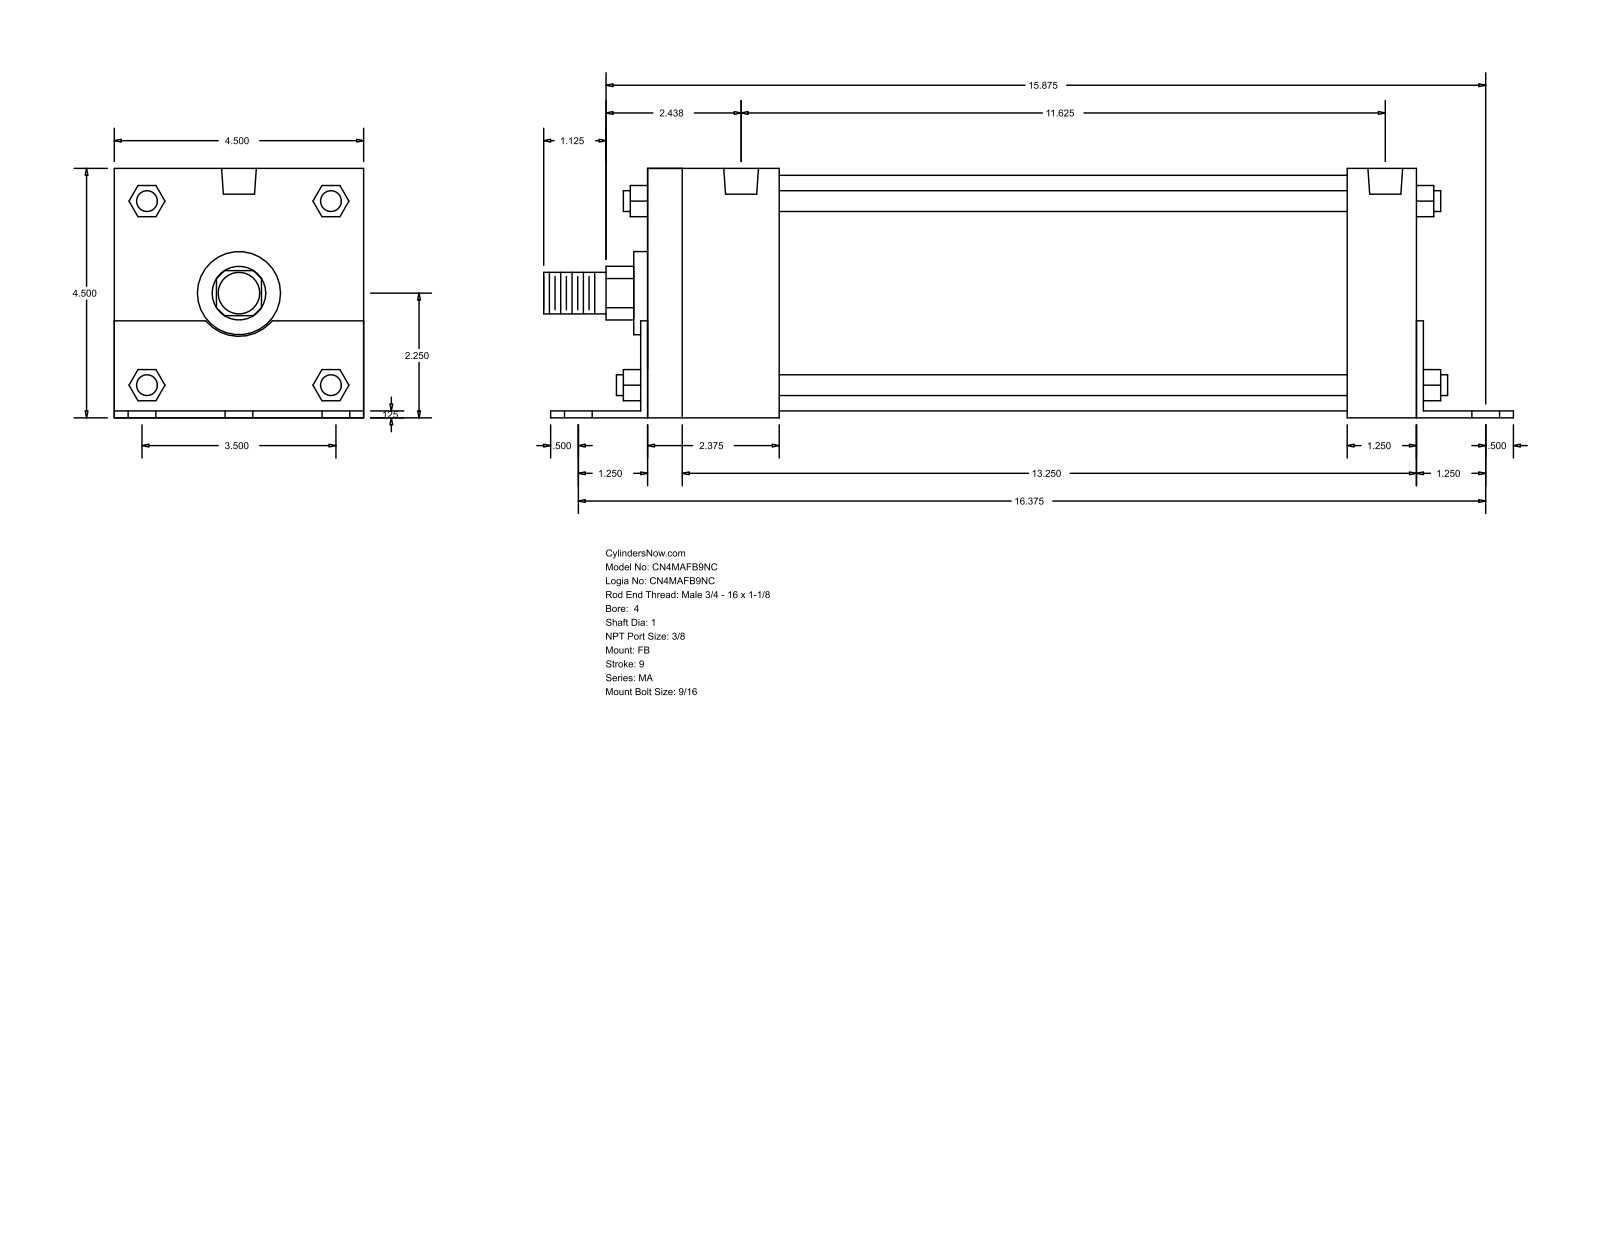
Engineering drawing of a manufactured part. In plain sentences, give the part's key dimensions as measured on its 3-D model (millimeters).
The part is named "MA_FB__0400_1". Its 3-D file was written by "GSSL Pune (CONFIG_CONTROL_DESIGN)". It is 0 solids with 140 faces: 105 planar, 35 cylindrical and 0 other. Overall it measures 444.5 by 114.35 by 114.3 millimeters. Round holes: 6 of diameter 14.29, 4 of diameter 11.11, 2 of diameter 15.93. Round bosses or shafts: 4 of diameter 9.53, 1 of diameter 107.95, 1 of diameter 38.1, 1 of diameter 25.4, 1 of diameter 19.05. Partial cylindrical surfaces (rounded edges, fillets, slot ends): 1 of radius 12.29, 1 of radius 19.81. The main face-to-face distances are 114.3, 3.17, 114.35, 355.6, 3.12, 111.18, 352.43, 358.77, 323.85, 320.68. The hole center spacings are 44.45, 418.3, 415.93, 4.76, 64, 67.5, 86.85, 88.9.
